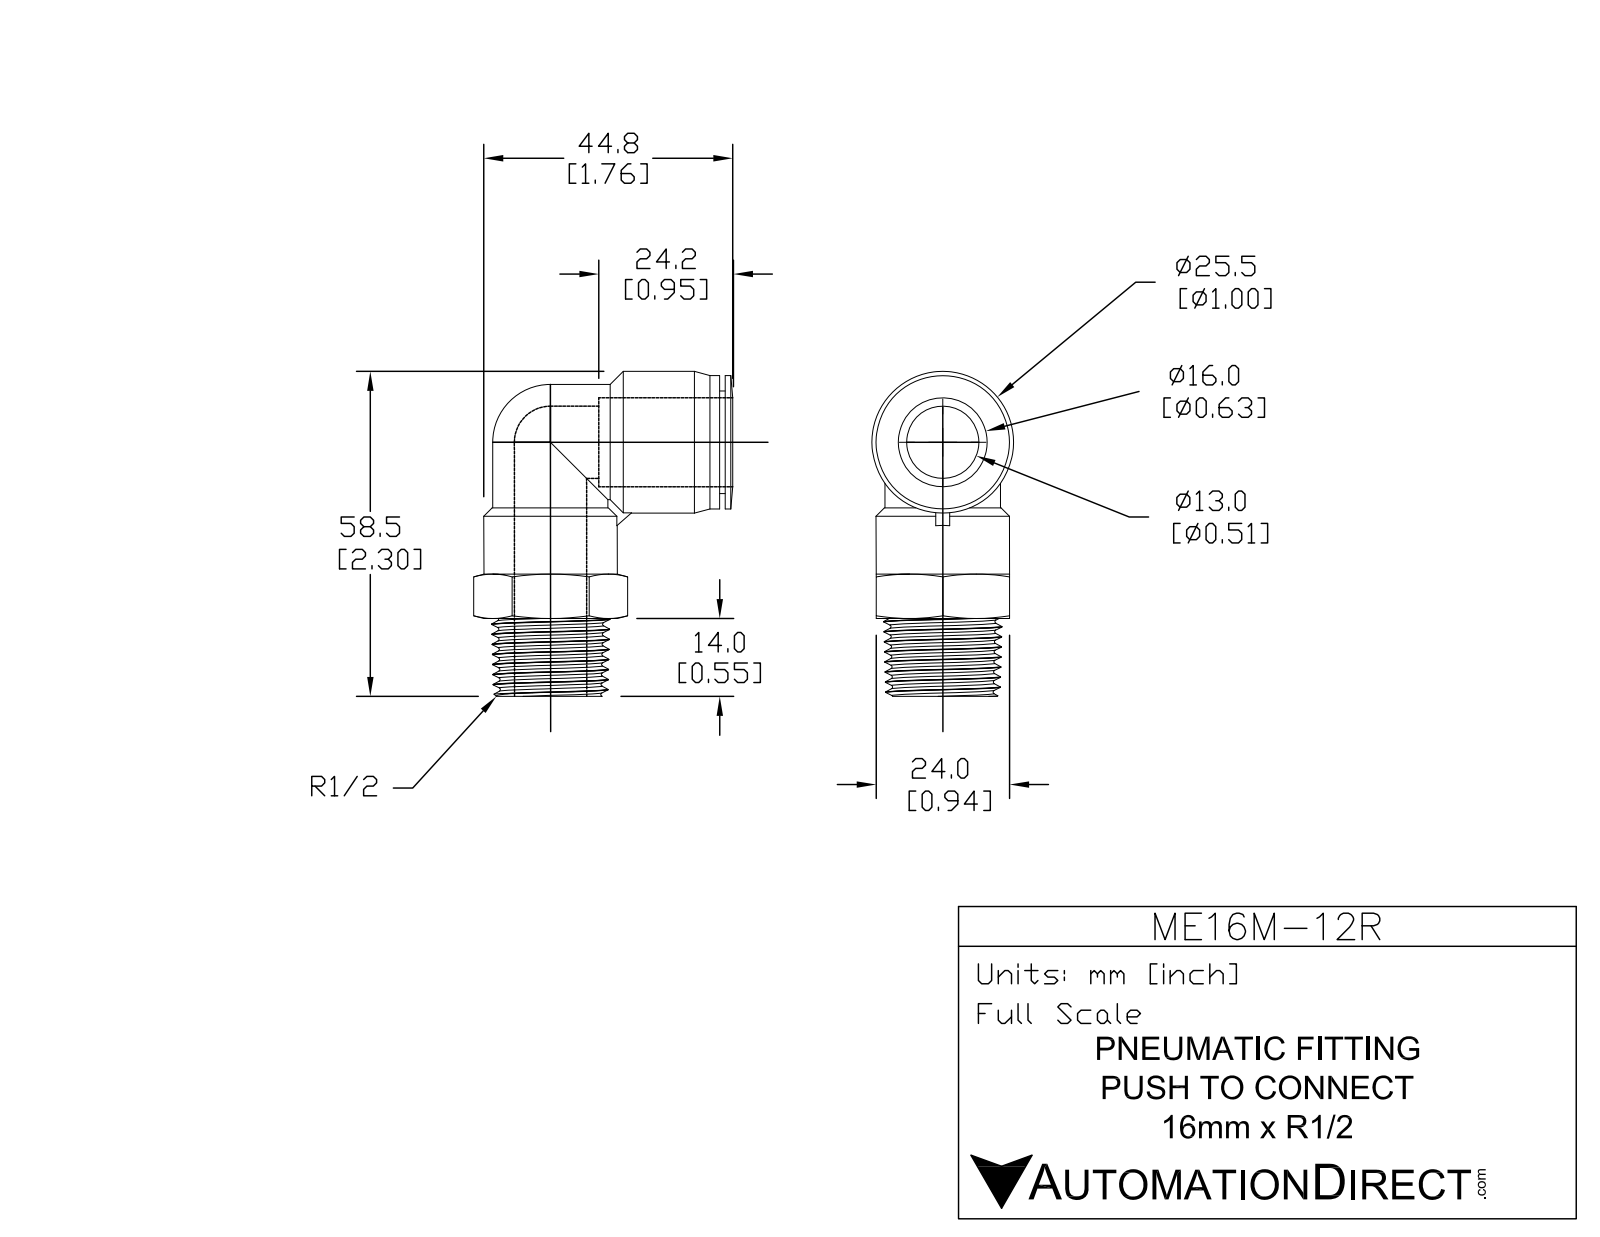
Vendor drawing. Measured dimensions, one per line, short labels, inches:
name: ME16M-12R
written by: SolidWorks 2015 (AUTOMOTIVE_DESIGN)
unit: in
bodies: 1 solid, 74 faces (14 planar, 22 cylindrical, 38 other)
size: 2.305 × 1.837 × 1.004
volume: 1.171 in³; area: 15.68 in²
holes: 2× ⌀0.512, 1× ⌀0.642
bosses: 2× ⌀0.803, 1× ⌀1.004, 1× ⌀0.992, 1× ⌀0.984, 1× ⌀0.945, 1× ⌀0.709
face distances: 0.945, 0.063, 0.551, 0.776, 0.839, 0.423, 0.522, 0.098
